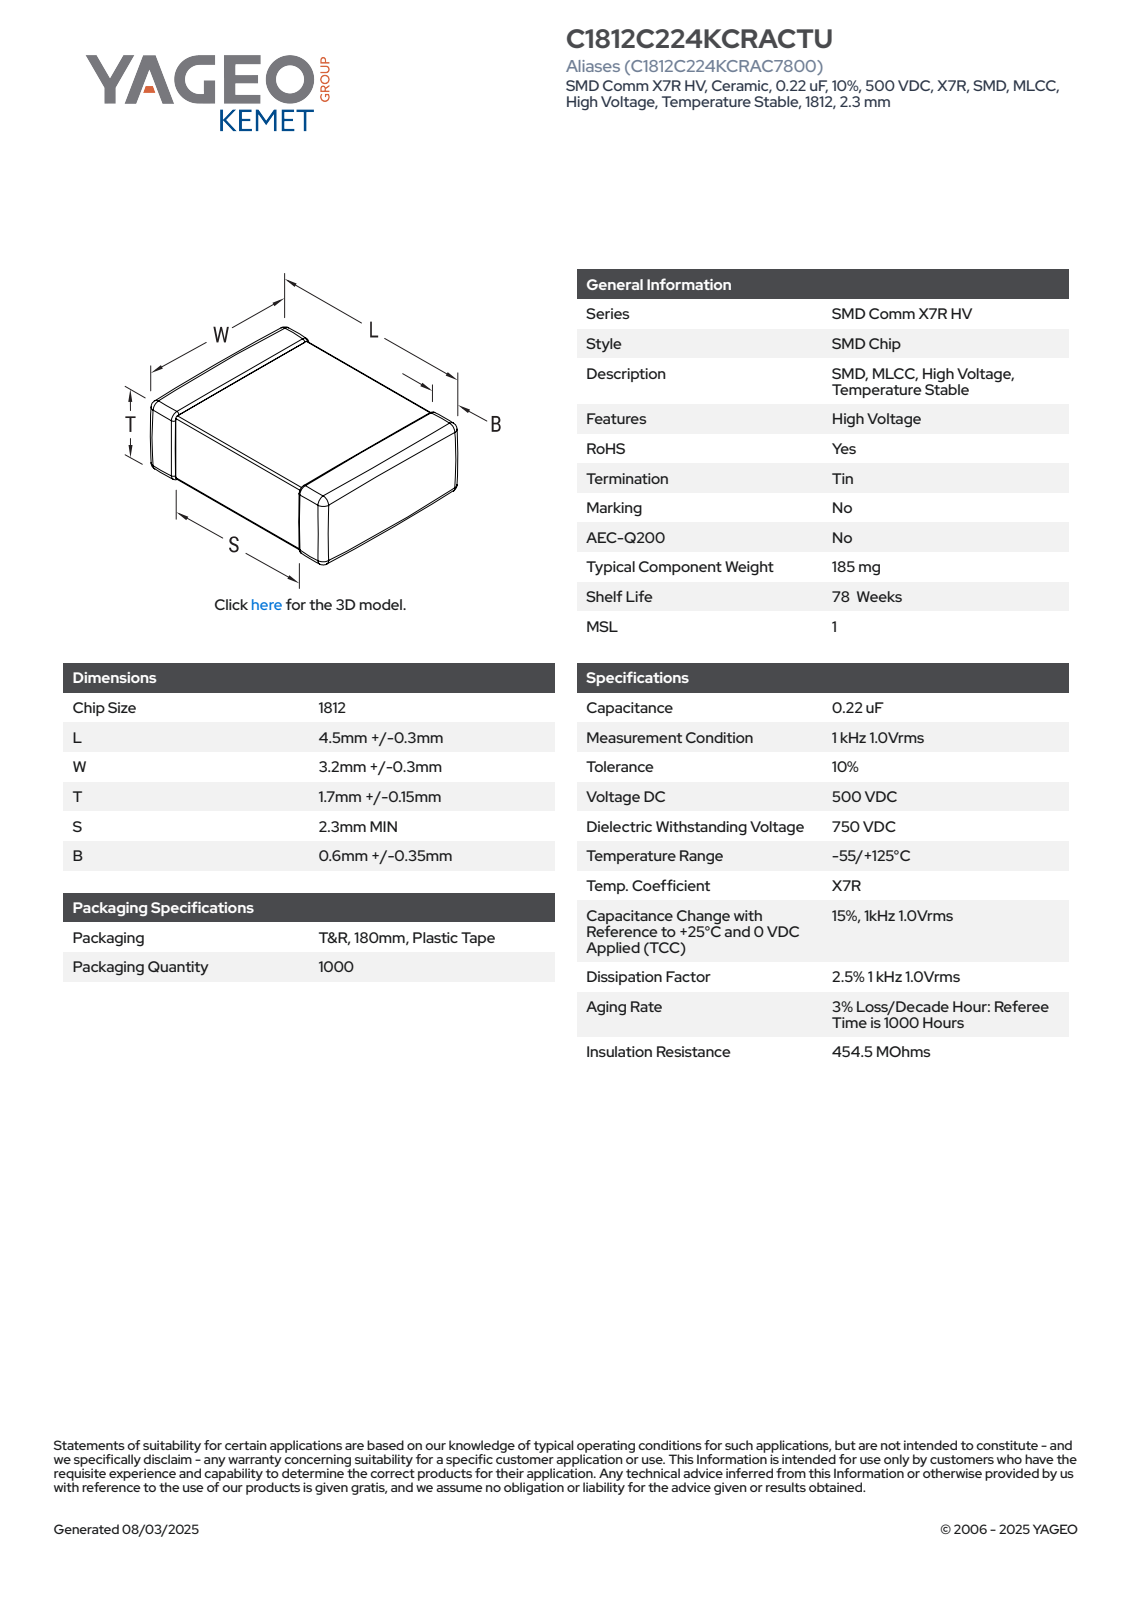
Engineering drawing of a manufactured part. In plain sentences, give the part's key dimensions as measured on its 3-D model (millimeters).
The part is named "CCS_CCSTDNOS_1812_L4.8W3.5T1.85B0.95". Its 3-D file was written by "SolidWorks 2014 (AUTOMOTIVE_DESIGN)". It is 4 solids with 121 faces: 71 planar, 34 cylindrical and 16 other. Overall it measures 4.8 by 3.5 by 1.85 millimeters. Its volume is 29 cubic millimeters and its surface area 63 square millimeters. The main face-to-face distances are 1.78, 1.71, 4.8, 3.43, 1.85, 3.36, 3.5, 1.49, 0.34, 1.94.
